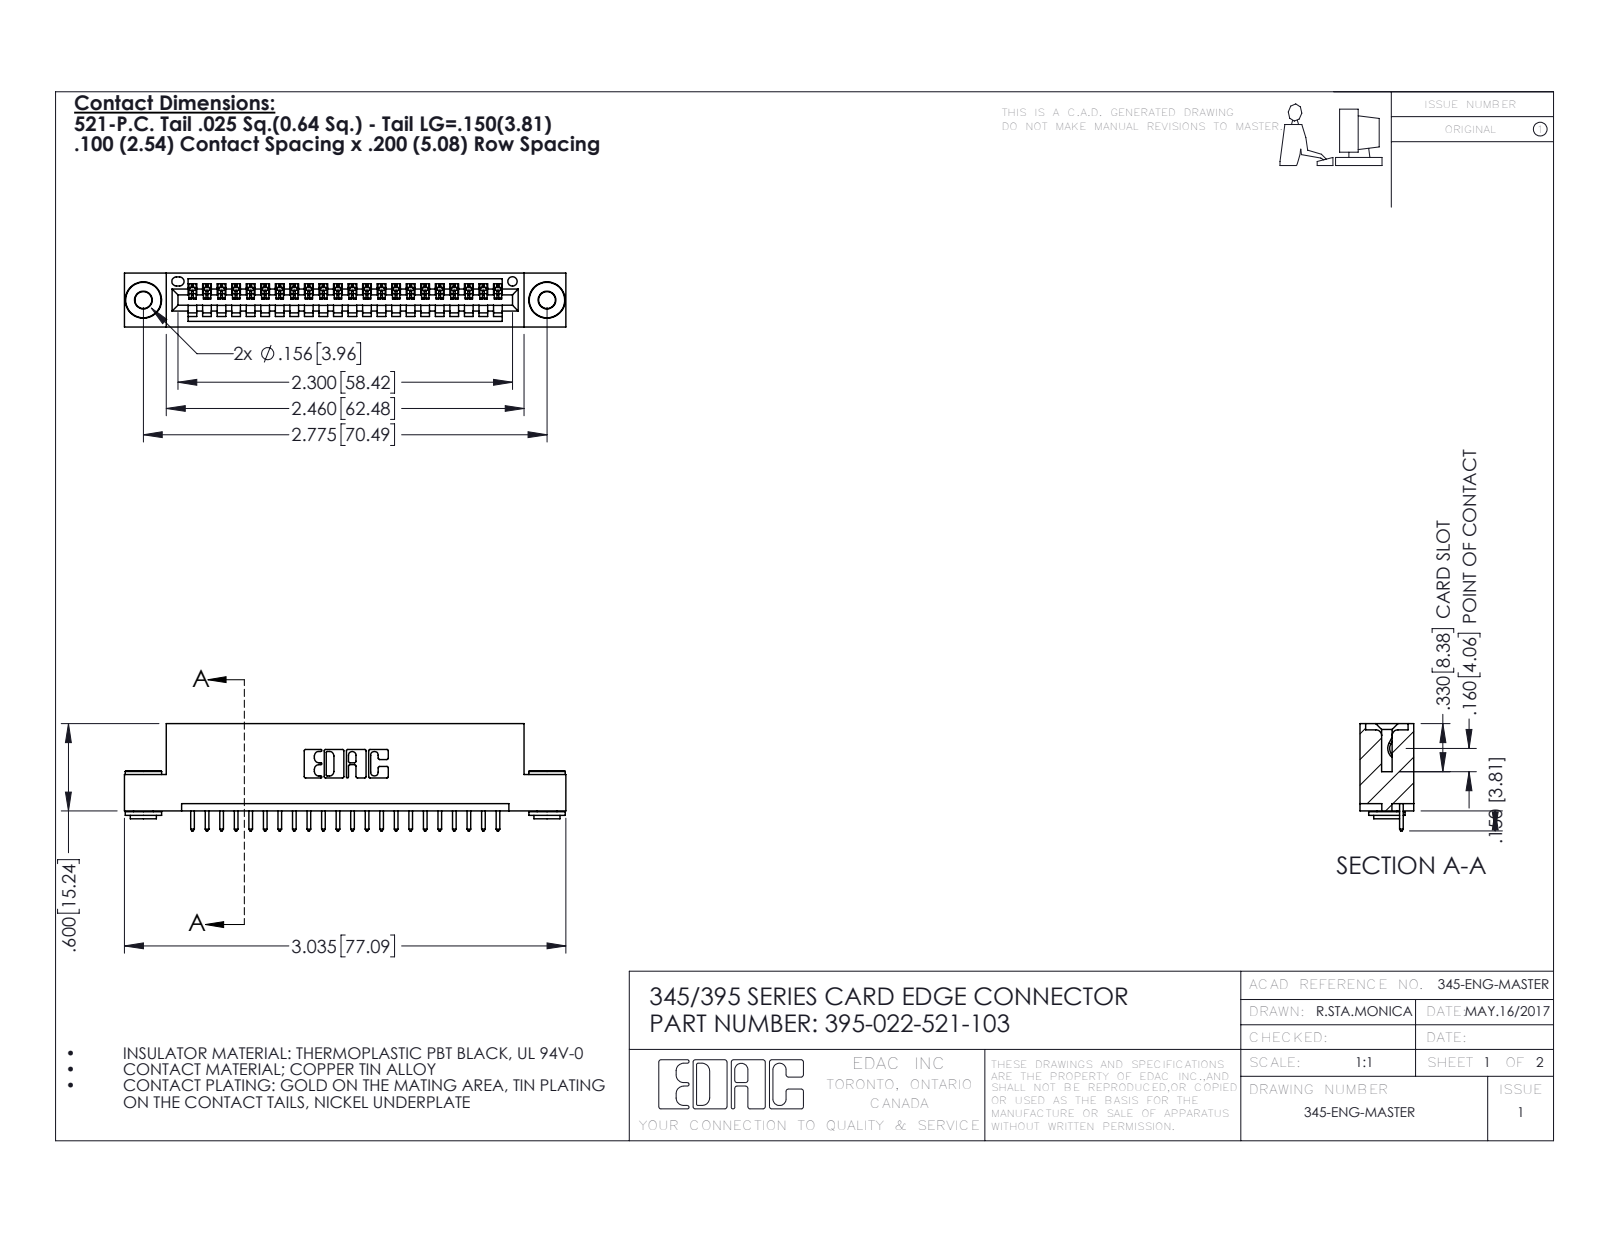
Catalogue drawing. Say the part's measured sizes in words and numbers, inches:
The part is named "345-250-002_345-250-002-102; 395-022-521-103; 345 Part_Flush Mounting Lugs - 0.156 Dia-TH; 345-292-001_345-293-121". Its 3-D file was written by "SolidWorks 2016 (CONFIG_CONTROL_DESIGN)". It is 25 solids with 1440 faces: 970 planar, 462 cylindrical and 8 other. Overall it measures 3.035 by 0.737 by 0.37 inches. Its volume is 0.434 cubic inches and its surface area 14.19 square inches. Round holes: 2 of diameter 0.116, 2 of diameter 0.156, 1 of diameter 0.064. Round bosses or shafts: 2 of diameter 0.25, 2 of diameter 0.18, 2 of diameter 0.136. Partial cylindrical surfaces (rounded edges, fillets, slot ends): 44 of radius 0.006, 44 of radius 0.01, 22 of radius 0.01, 6 of radius 0.007, 6 of radius 0.031, 3 of radius 0.026, 2 of radius 0.031, 2 of radius 0.04. The main face-to-face distances are 0.072, 0.298, 0.2, 0.37, 0.025, 0.098, 0.272, 0.225, 0.149, 0.072. The hole center spacings are 0.27, 2.541, 2.775.
